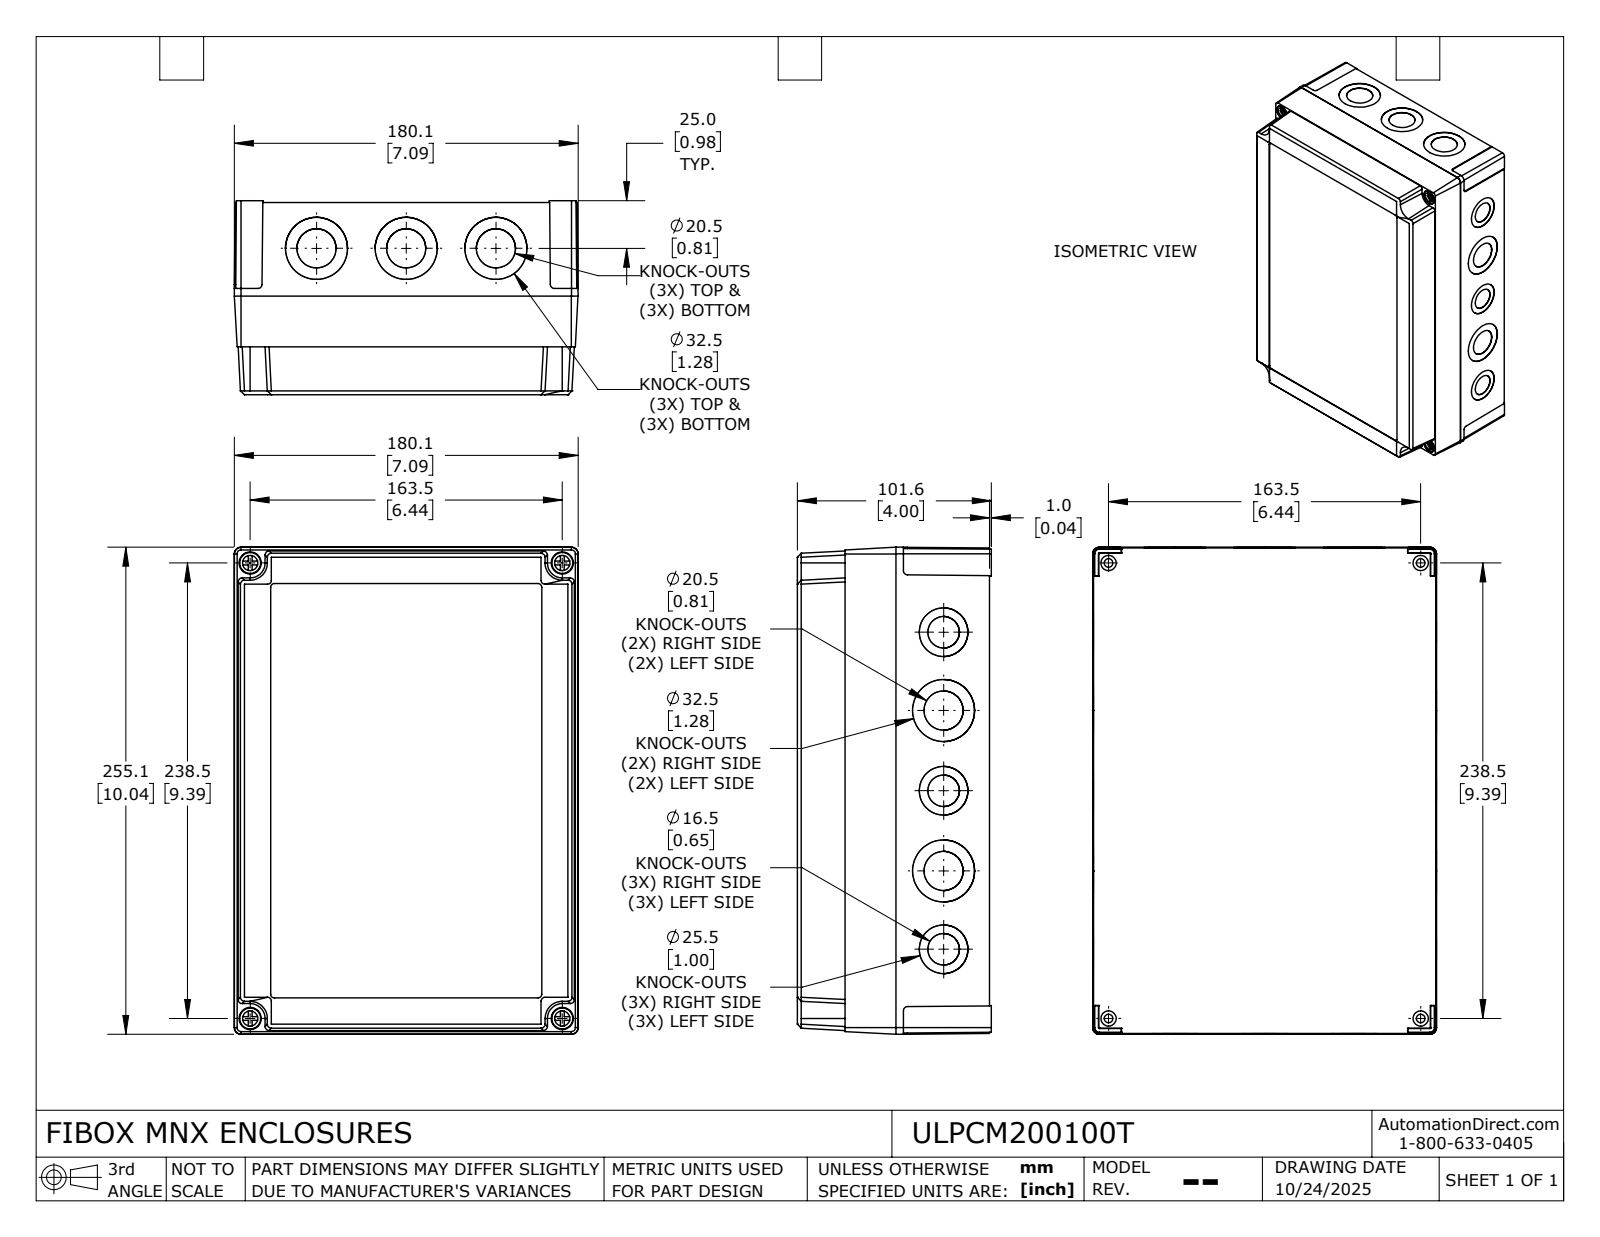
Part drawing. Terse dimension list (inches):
name: ULPCM200100T_Default
written by: SolidWorks 2024 (CONFIG_CONTROL_DESIGN)
unit: in
bodies: 6 solids, 725 faces (383 planar, 280 cylindrical, 62 other)
size: 10.043 × 7.091 × 4
volume: 31.23 in³; area: 562.1 in²
holes: 20× ⌀0.126, 20× ⌀0.157, 10× ⌀0.807, 10× ⌀1.28, 6× ⌀0.65, 6× ⌀1.004, 4× ⌀0.177, 4× ⌀0.315, 4× ⌀0.457
bosses: 16× ⌀0.315, 4× ⌀0.433, 4× ⌀0.283, 4× ⌀0.276
rounds: 8× R0.079, 8× R0.083, 6× R0.112, 4× R0.042, 4× R0.197, 2× R0.046
face distances: 3.858, 0.118, 3.74, 3.941, 3.823, 0.083, 0.165, 0.077, 0.055, 0.022
hole spacings: 4.921, 1.939, 5.046, 0.812, 0.872, 1.046, 1.333, 1.508
